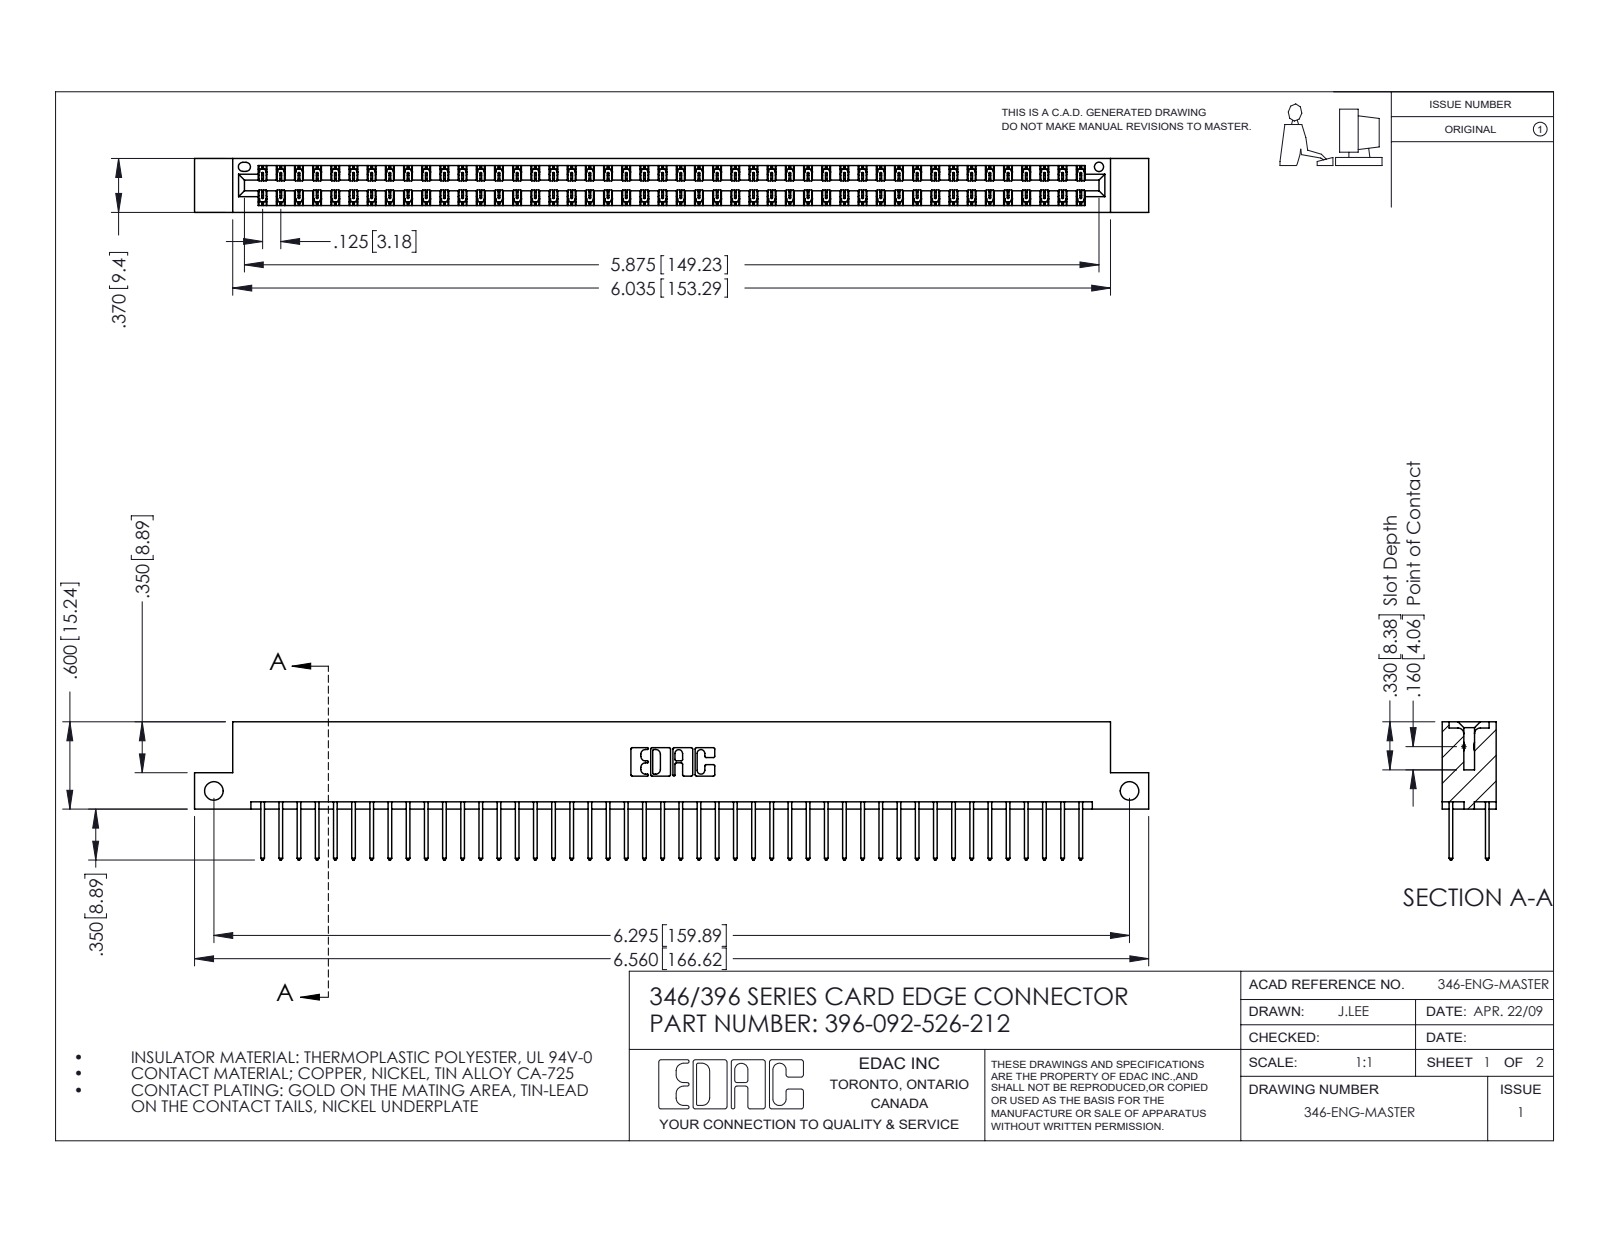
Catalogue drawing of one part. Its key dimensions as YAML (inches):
part_name: "345-292-001_345-293-126; 396-092-526-212; 346 Part_Flush Mounting Lugs - Side Mount"
step_written_by: "SolidWorks 2016 (CONFIG_CONTROL_DESIGN)"
units: inches
bodies: {solids: 93, faces: 4906, planar: 3296, cylindrical: 1610, other: 0}
overall_size: [6.56, 0.95, 0.37]
volume: 0.997
surface_area: 35.75
round_holes:
  - {diameter: 0.128, count: 2}
  - {diameter: 0.064, count: 1}
partial_cylinders:
  - {radius: 0.006, count: 138}
  - {radius: 0.01, count: 92}
  - {radius: 0.01, count: 22}
  - {radius: 0.007, count: 6}
  - {radius: 0.031, count: 6}
  - {radius: 0.026, count: 3}
  - {radius: 0.014, count: 2}
  - {radius: 0.022, count: 2}
face_to_face_distances: [0.048, 0.322, 0.25, 0.37, 0.072, 0.298, 0.025, 0.275, 0.148, 0.222]
hole_center_spacings: [6.295]
